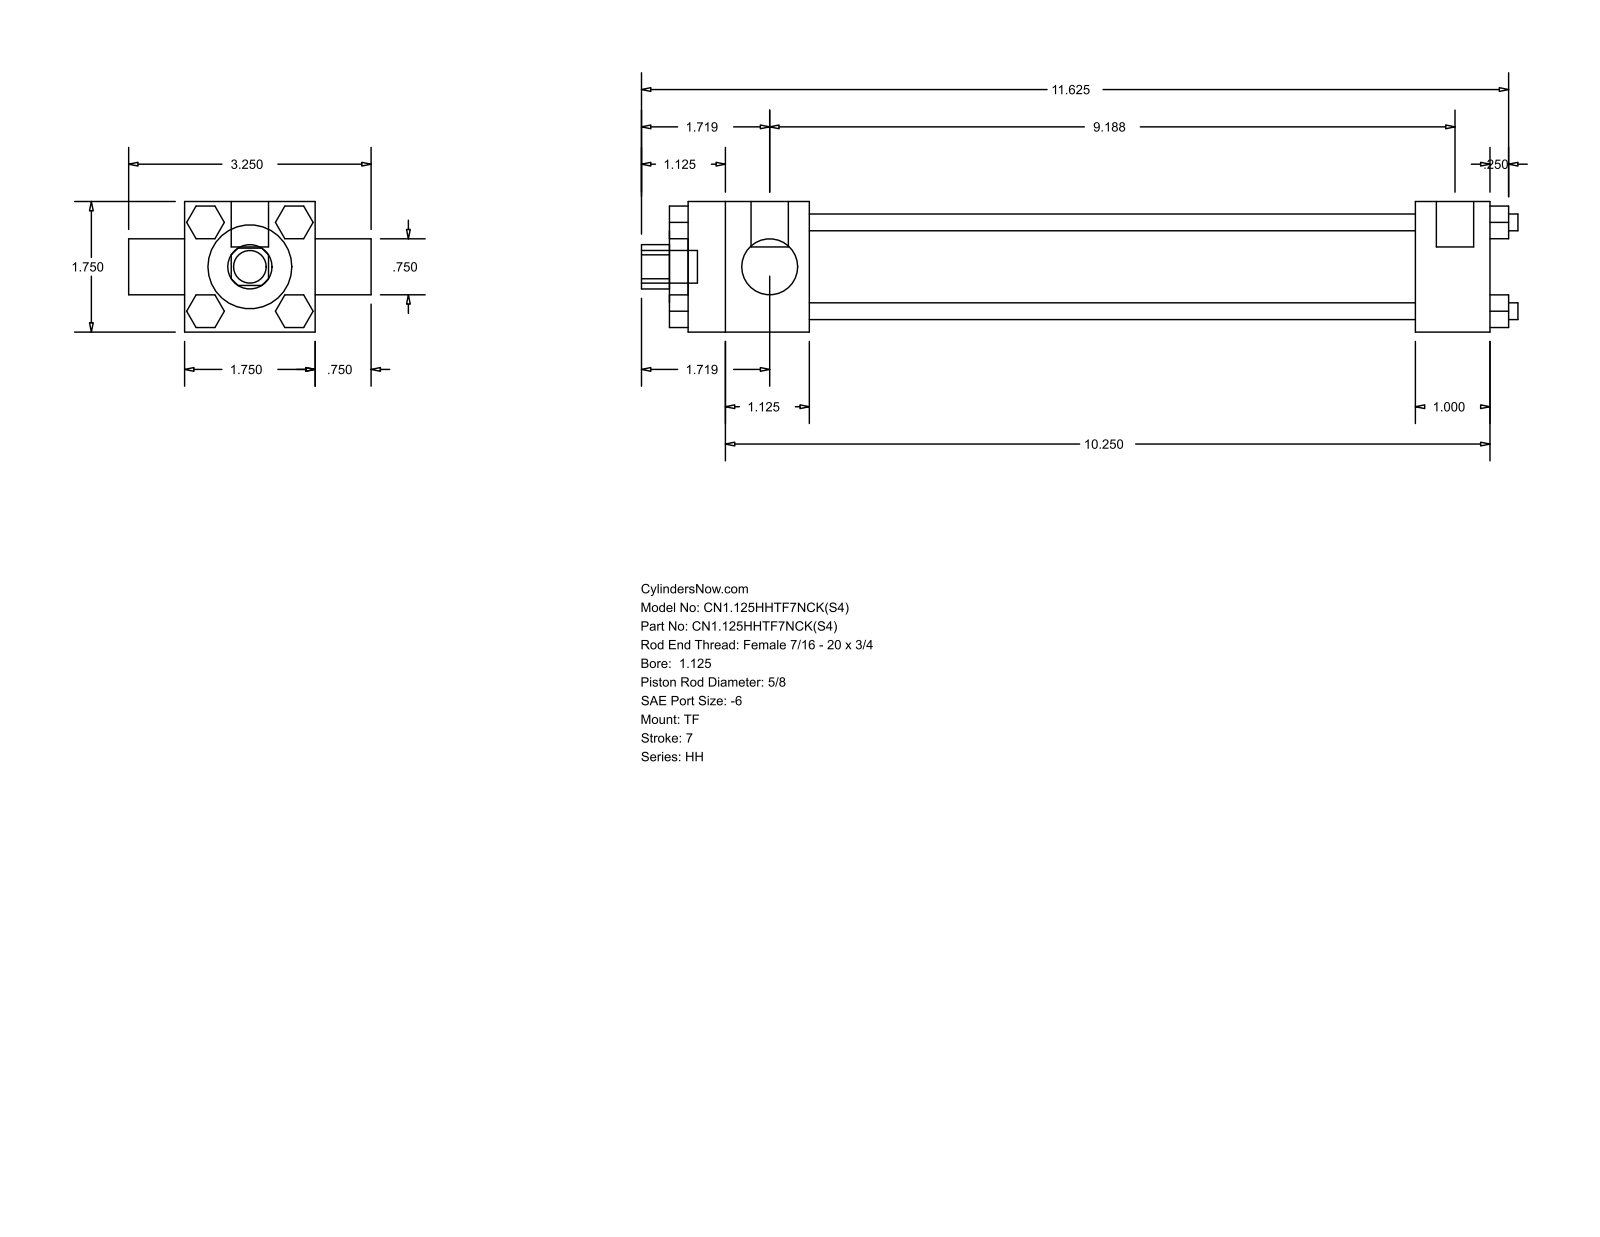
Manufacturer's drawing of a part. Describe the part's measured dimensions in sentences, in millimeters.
The part is named "HH_TF__0112_0.625". Its 3-D file was written by "GSSL Pune (CONFIG_CONTROL_DESIGN)". It is 0 solids with 120 faces: 92 planar, 28 cylindrical and 0 other. Overall it measures 298.45 by 82.55 by 44.45 millimeters. Round holes: 1 of diameter 15.88, 1 of diameter 19.05, 1 of diameter 28.57, 1 of diameter 34.92. Round bosses or shafts: 4 of diameter 5.71, 3 of diameter 5.56, 2 of diameter 12.7, 1 of diameter 11.11. Partial cylindrical surfaces (rounded edges, fillets, slot ends): 1 of radius 7.54. The main face-to-face distances are 44.46, 11.11, 206.37, 231.78, 25.41, 41.27, 247.64, 273.05, 47.62, 279.4.
